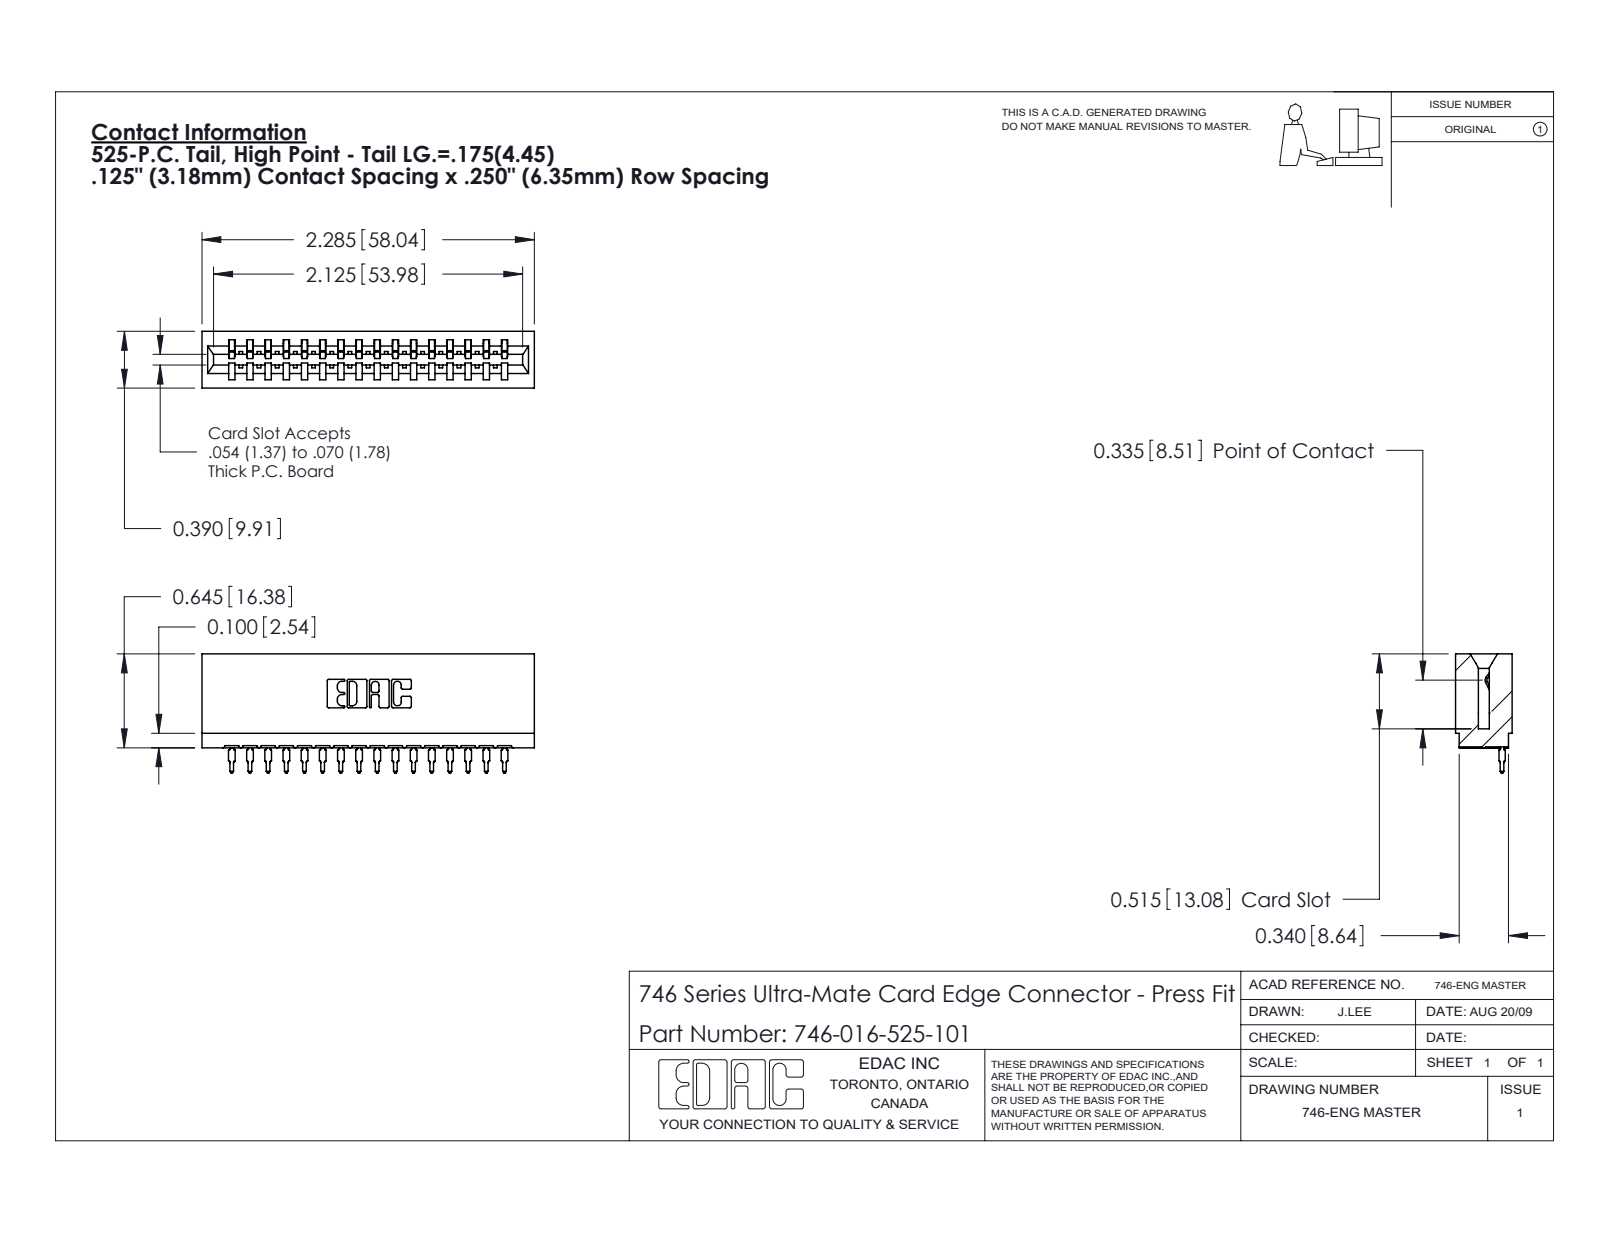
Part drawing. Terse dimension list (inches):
name: 746-016-525-101; 746-292-001_525; 746 Part_.515 Slot Depth - 01
written by: SolidWorks 2020 (CONFIG_CONTROL_DESIGN)
unit: in
bodies: 17 solids, 1825 faces (1063 planar, 346 cylindrical, 416 other)
size: 2.285 × 0.819 × 0.39
volume: 0.38 in³; area: 13.5 in²
rounds: 32× R0.021, 22× R0.01, 17× R0.015, 6× R0.007, 6× R0.031, 4× R0.005, 4× R0.011, 3× R0.026
face distances: 0.25, 0.333, 0.057, 0.5, 0.39, 0.125, 0.042, 0.208, 0.125, 0.292
